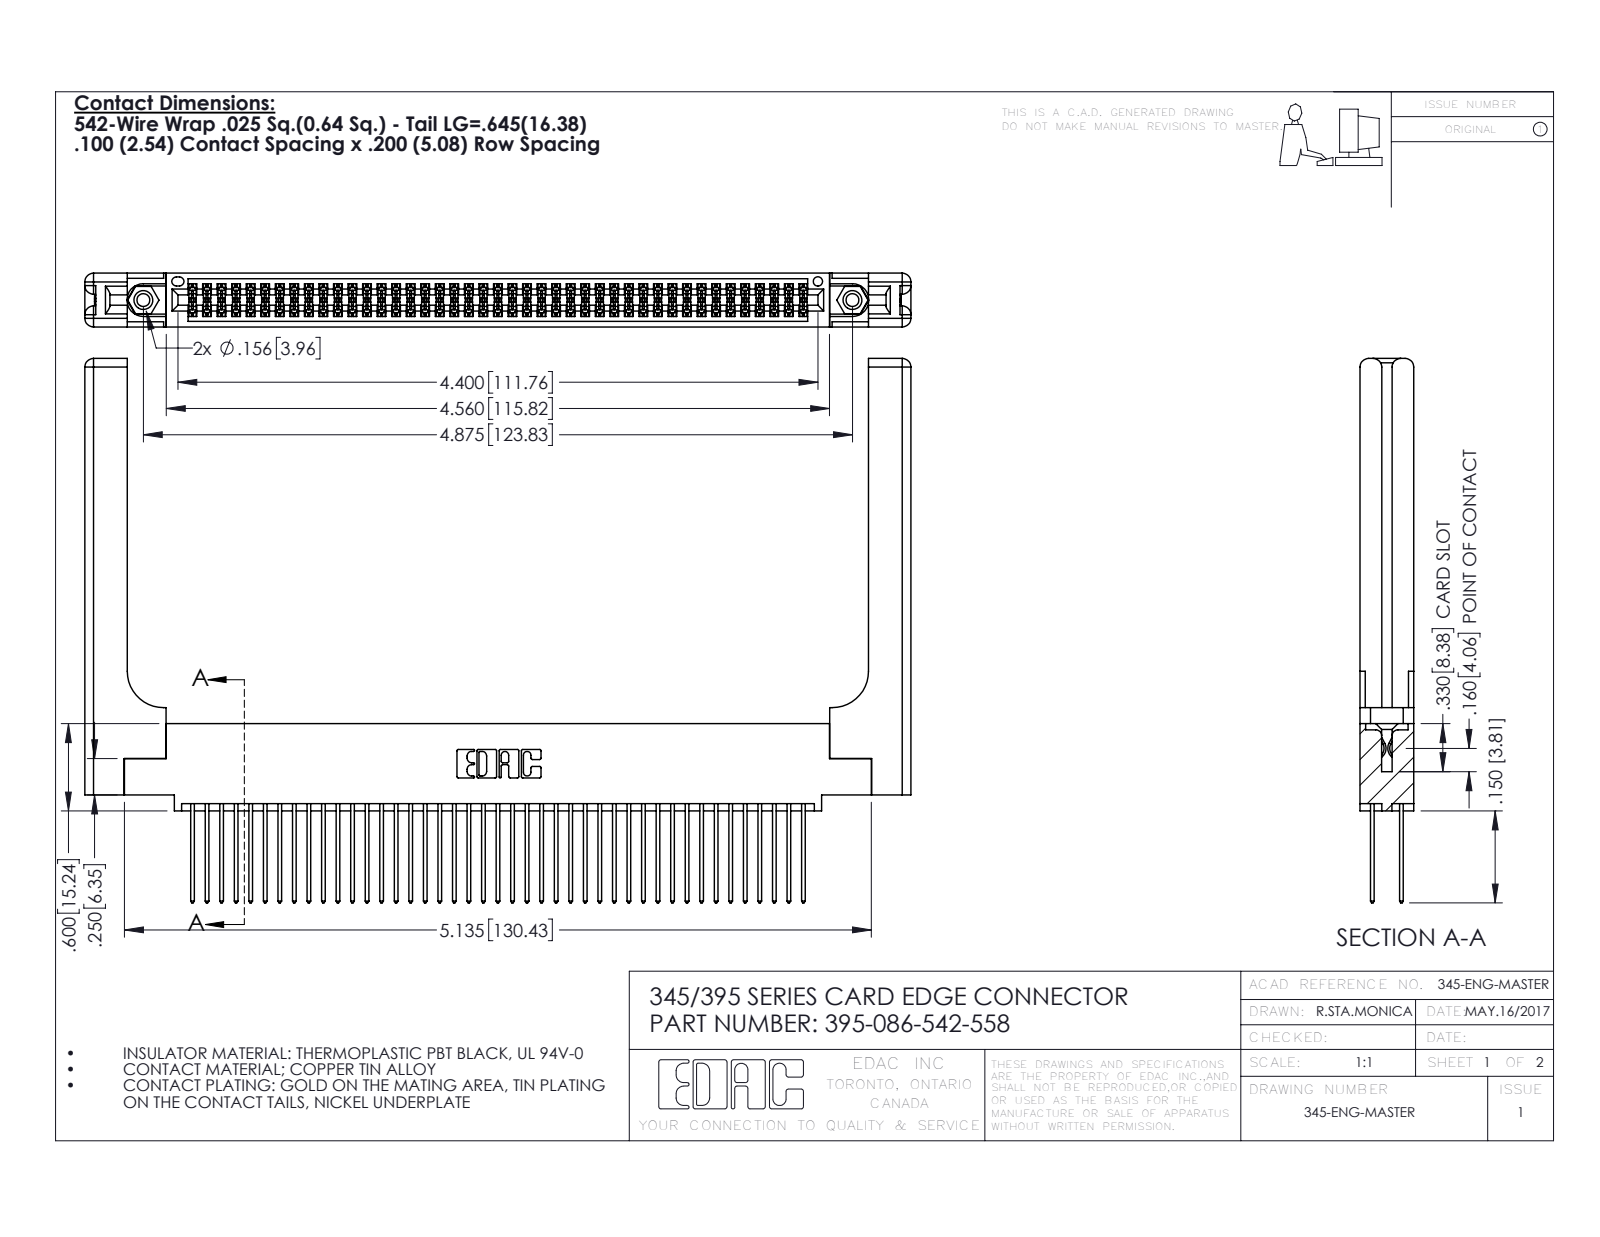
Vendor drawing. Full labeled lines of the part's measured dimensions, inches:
Part name (STEP PRODUCT): 345-292-001_345-293-142; 345-220-058_345-220-058; 345 Part_0.110 Offset - 0.156 Dia-TH; 395-086-542-558 (+1 more)
STEP written by: SolidWorks 2016 (CONFIG_CONTROL_DESIGN)
Units: inches
Bodies: 91 solids, 4686 faces (3070 planar, 1556 cylindrical, 60 other)
Overall size (bounding box): 5.679 × 3.742 × 0.37
Volume: 1.393 in³ · Surface area: 43.8 in²
Round holes (diameter × count): ⌀0.089 ×2, ⌀0.125 ×2, ⌀0.156 ×2, ⌀0.064 ×1
Round bosses / shafts (diameter × count): ⌀0.155 ×2
Partial cylindrical surfaces — rounded edges, fillets, slot ends (radius × count): R0.006 ×129, R0.01 ×86, R0.01 ×22, R0.06 ×16, R0.007 ×6, R0.031 ×6, R0.026 ×3, R0.014 ×2
Main face-to-face distances: 0.072, 0.298, 0.37, 0.098, 0.272, 0.025, 0.2, 0.225, 0.175, 0.148
Hole centre spacings: 0.27, 4.639, 4.875
